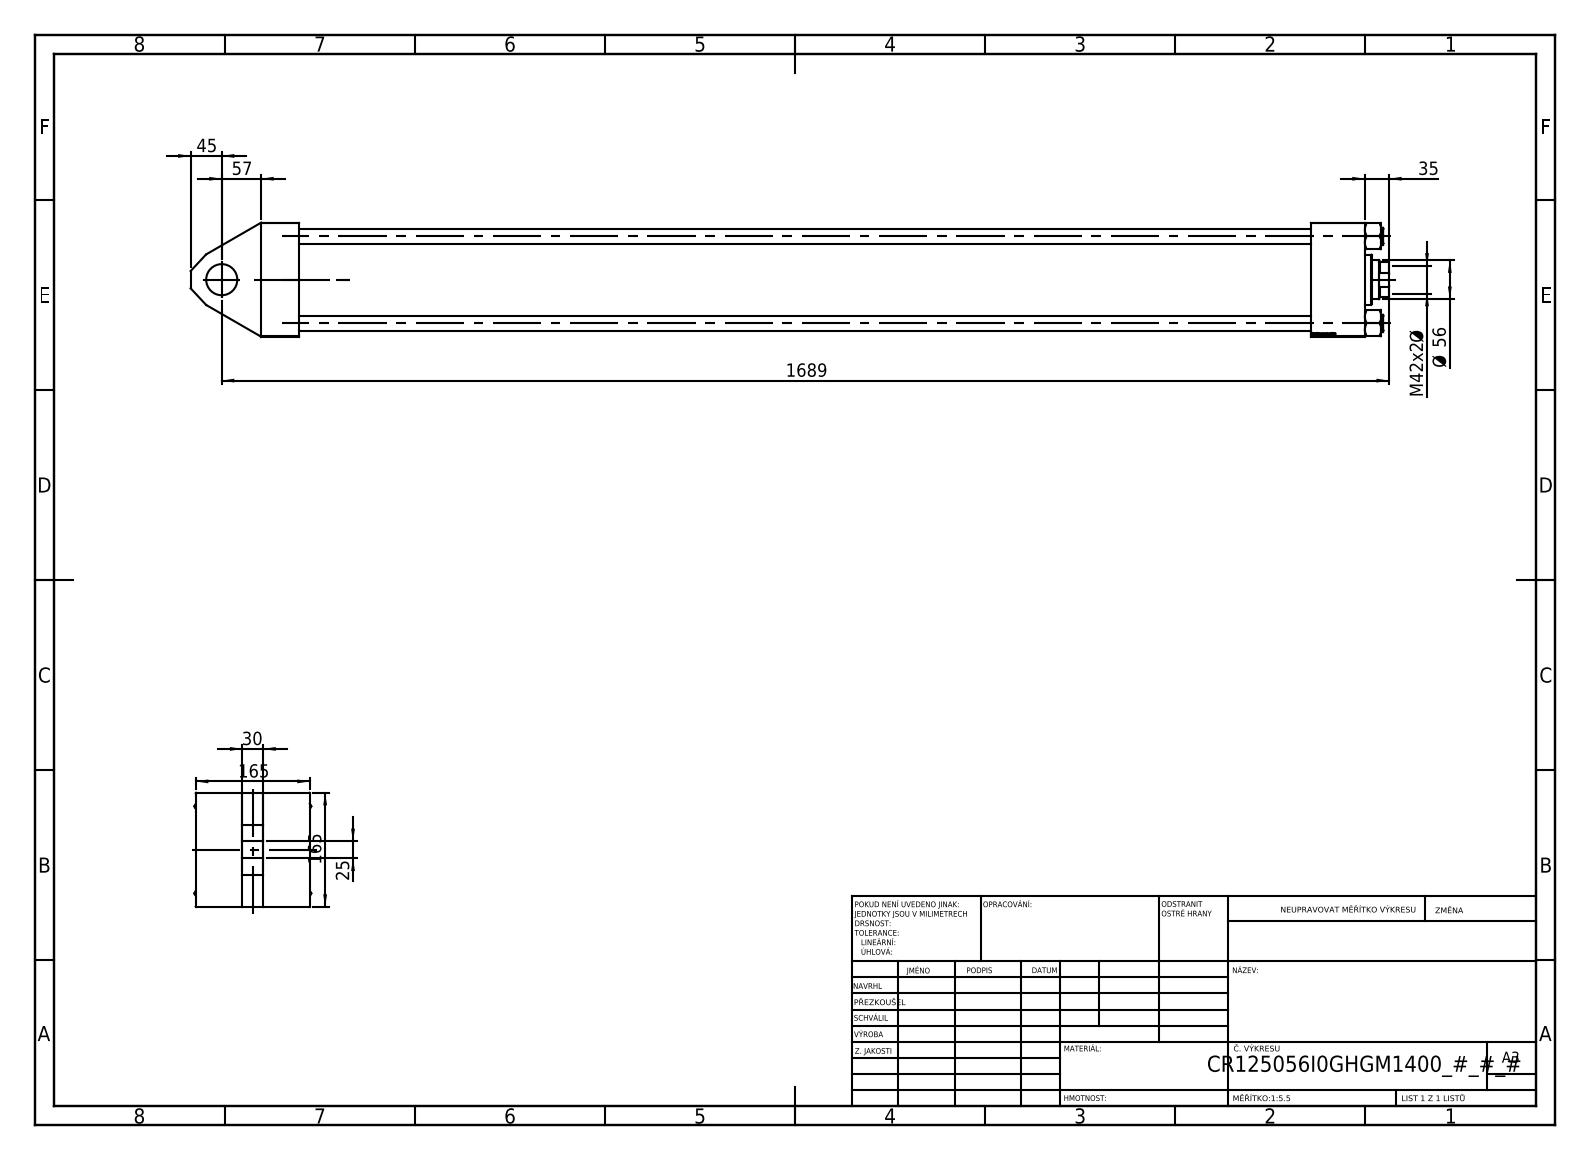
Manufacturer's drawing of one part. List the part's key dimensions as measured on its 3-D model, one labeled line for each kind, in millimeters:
Part name (STEP PRODUCT): V215_VC_A; V215CR_VCP_I; V215CR_TYCINKA_I; V215CR_I_Body (+1 more)
STEP written by: SolidWorks 2019 (CONFIG_CONTROL_DESIGN)
Units: millimetres
Bodies: 11 solids, 1127 faces (550 planar, 81 cylindrical, 496 other)
Overall size (bounding box): 1734 × 169.14 × 165
Volume: 11 970 000 mm³ · Surface area: 2 268 000 mm²
Round holes (diameter × count): ⌀22 ×4, ⌀45 ×3, ⌀7 ×2, ⌀32.24 ×2, ⌀40.5 ×1, ⌀56 ×1, ⌀59 ×1, ⌀96 ×1, ⌀125 ×1, ⌀125.5 ×1
Round bosses / shafts (diameter × count): ⌀25 ×4, ⌀131 ×1, ⌀72 ×1
Partial cylindrical surfaces — rounded edges, fillets, slot ends (radius × count): R27 ×1
Main face-to-face distances: 165, 1542, 55, 1597, 78, 67.5, 97.5, 1519, 1464, 1568.3
Hole centre spacings: 89.02, 125.9, 178.05, 84.5, 1518.5, 1603
